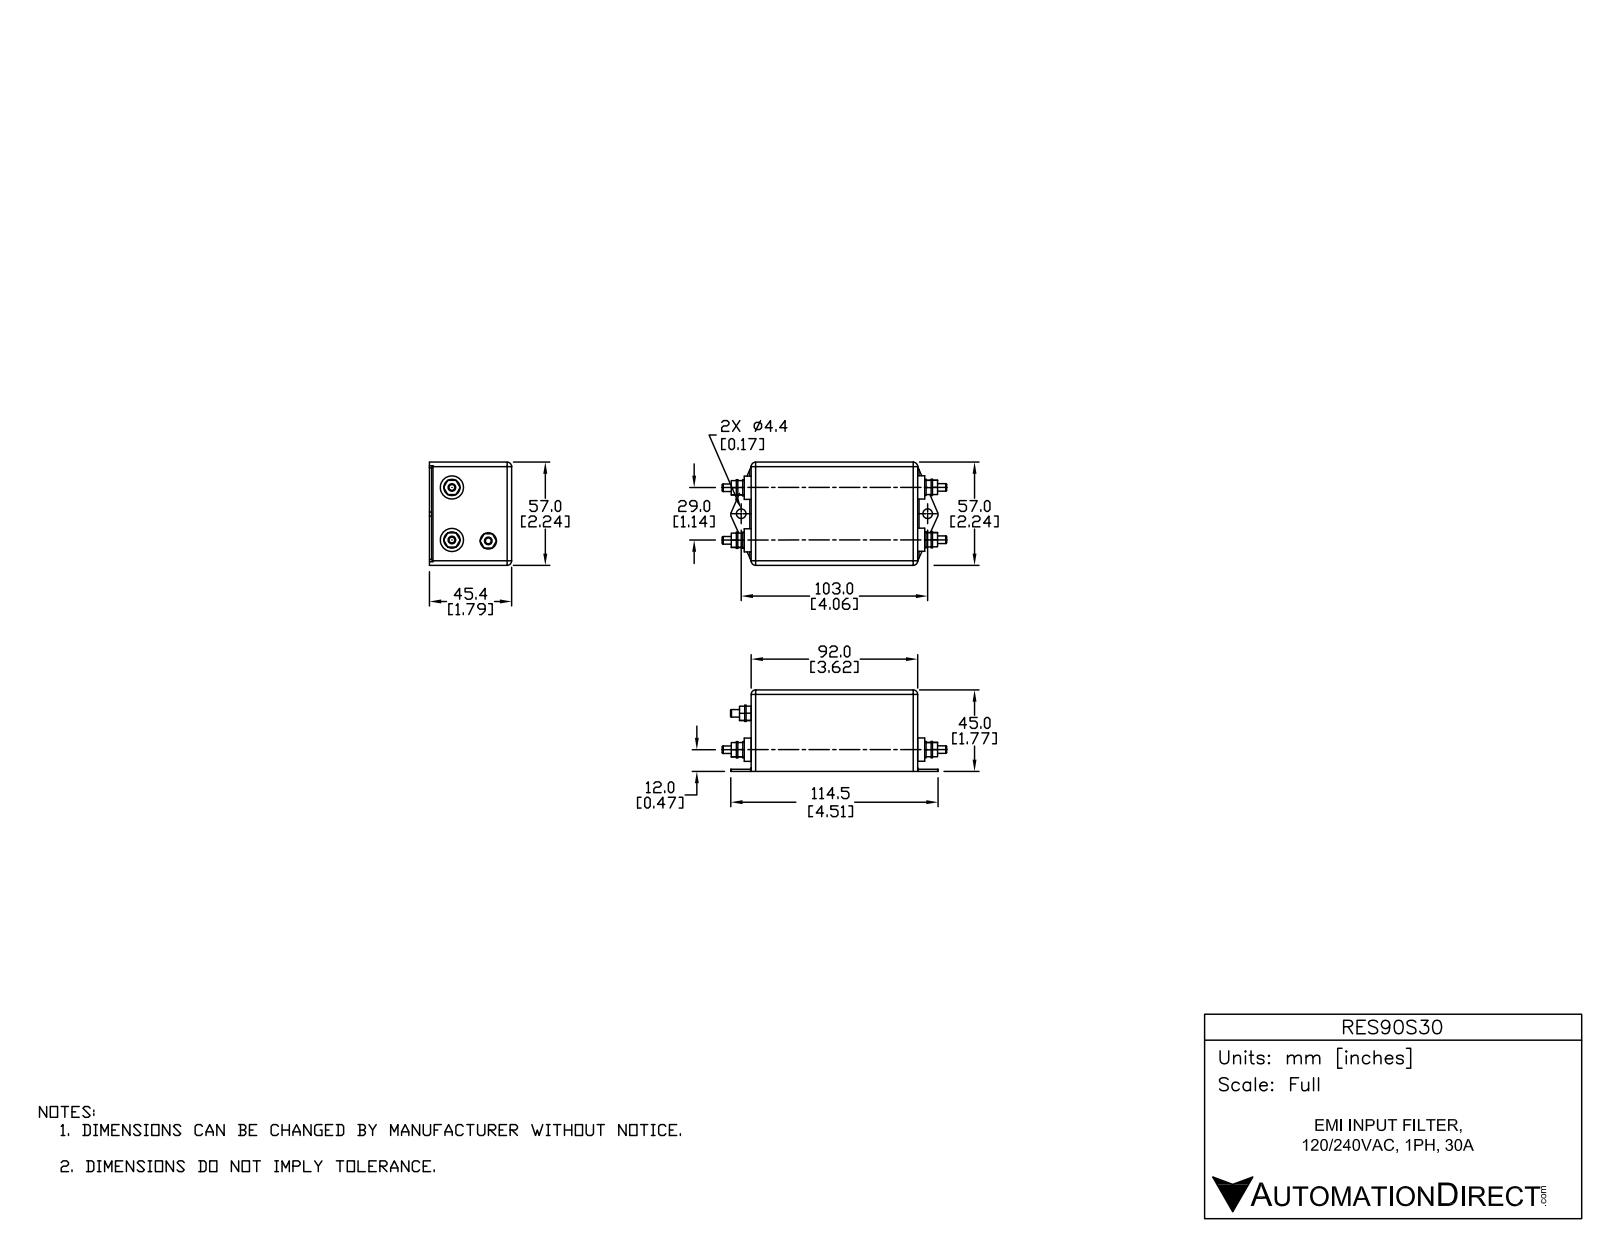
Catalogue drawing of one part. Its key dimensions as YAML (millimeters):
part_name: "RES90S30"
step_written_by: "SolidWorks 2015 (AUTOMOTIVE_DESIGN)"
units: millimeters
bodies: {solids: 1, faces: 52, planar: 17, cylindrical: 29, other: 6}
overall_size: [114.43, 57, 45]
volume: 236056
surface_area: 24478
round_holes:
  - {diameter: 5.3, count: 2}
  - {diameter: 2, count: 1}
round_bosses_or_shafts:
  - {diameter: 12.8, count: 2}
partial_cylinders:
  - {radius: 5, count: 12}
  - {radius: 2.5, count: 2}
  - {radius: 0.75, count: 1}
face_to_face_distances: [45, 57, 92, 3.8, 95.8, 1.2, 43.8, 99.6, 95.7, 91.9]
hole_center_spacings: [103]
